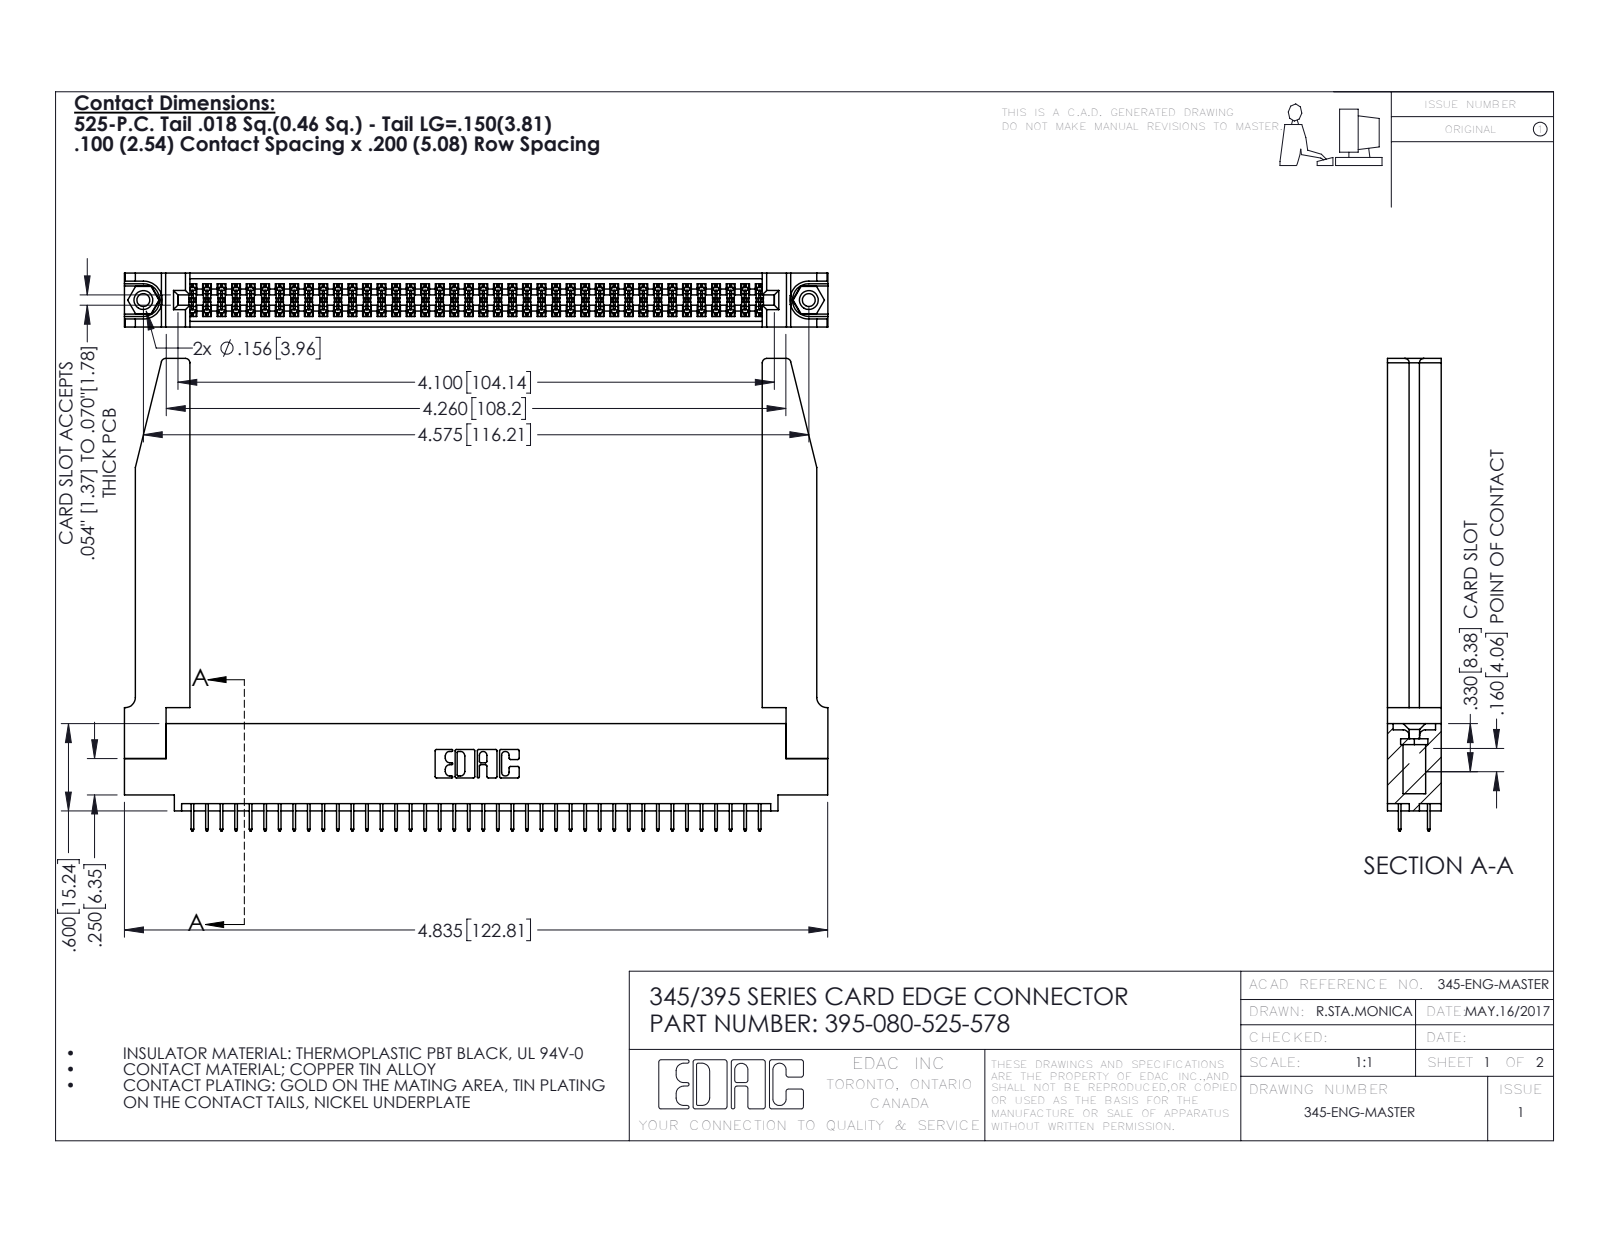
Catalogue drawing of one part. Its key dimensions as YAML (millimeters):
part_name: "345-220-078_345-220-078; 345-292-001_345-293-125; 395-080-525-578; 345 Part_0.110 Offset - 0.156 Dia-TH (+1 more)"
step_written_by: "SolidWorks 2020 (CONFIG_CONTROL_DESIGN)"
units: millimeters
bodies: {solids: 85, faces: 4684, planar: 3346, cylindrical: 1286, other: 52}
overall_size: [122.8, 82.5, 9.4]
volume: 19480
surface_area: 23800
round_holes:
  - {diameter: 2.3, count: 2}
  - {diameter: 3.2, count: 2}
  - {diameter: 4, count: 2}
  - {diameter: 1.6, count: 1}
round_bosses_or_shafts:
  - {diameter: 3.9, count: 2}
partial_cylinders:
  - {radius: 0.2, count: 120}
  - {radius: 0.3, count: 22}
  - {radius: 0.8, count: 8}
  - {radius: 0.2, count: 6}
  - {radius: 0.8, count: 6}
  - {radius: 0.7, count: 3}
  - {radius: 0.4, count: 2}
  - {radius: 0.5, count: 2}
face_to_face_distances: [9.4, 1.8, 7.6, 5.1, 2.5, 6.9, 0.6, 5.7, 3.8, 3.8]
hole_center_spacings: [6.9, 110.2, 116.2]
